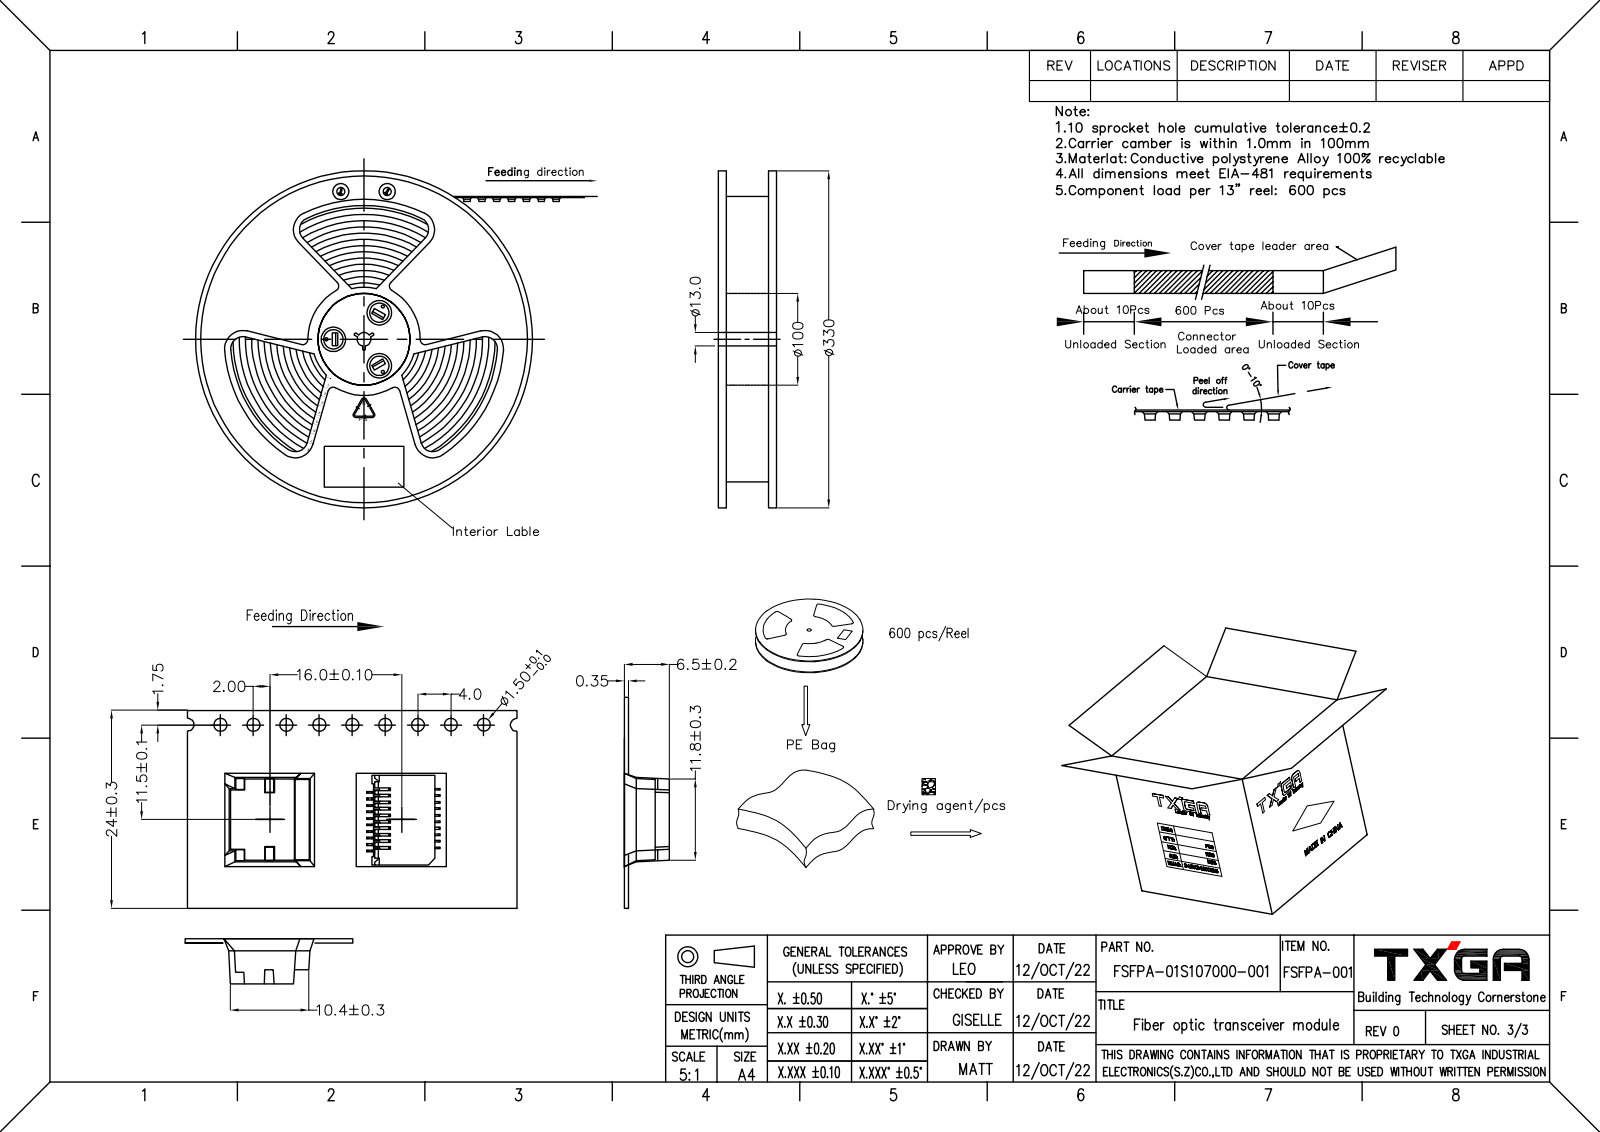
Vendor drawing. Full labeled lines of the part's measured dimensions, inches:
Part name (STEP PRODUCT): SFP-DUANZI; JINZHEN; SFP1X1_ASM
STEP written by: CREO PARAMETRIC BY PTC INC, 2020033 (CONFIG_CONTROL_DESIGN)
Units: inches
Bodies: 21 solids, 1150 faces (833 planar, 311 cylindrical, 6 other)
Overall size (bounding box): 0.433 × 0.354 × 0.246
Volume: 0.02 in³ · Surface area: 1.26 in²
Round bosses / shafts (diameter × count): ⌀0.055 ×1
Partial cylindrical surfaces — rounded edges, fillets, slot ends (radius × count): R0.006 ×14, R0.004 ×8, R0.008 ×3, R0.012 ×1, R0.016 ×1, R0.018 ×1, R0.02 ×1, R0.028 ×1
Main face-to-face distances: 0.094, 0.031, 0.063, 0.051, 0.189, 0.126, 0.144, 0.043, 0.157, 0.433
